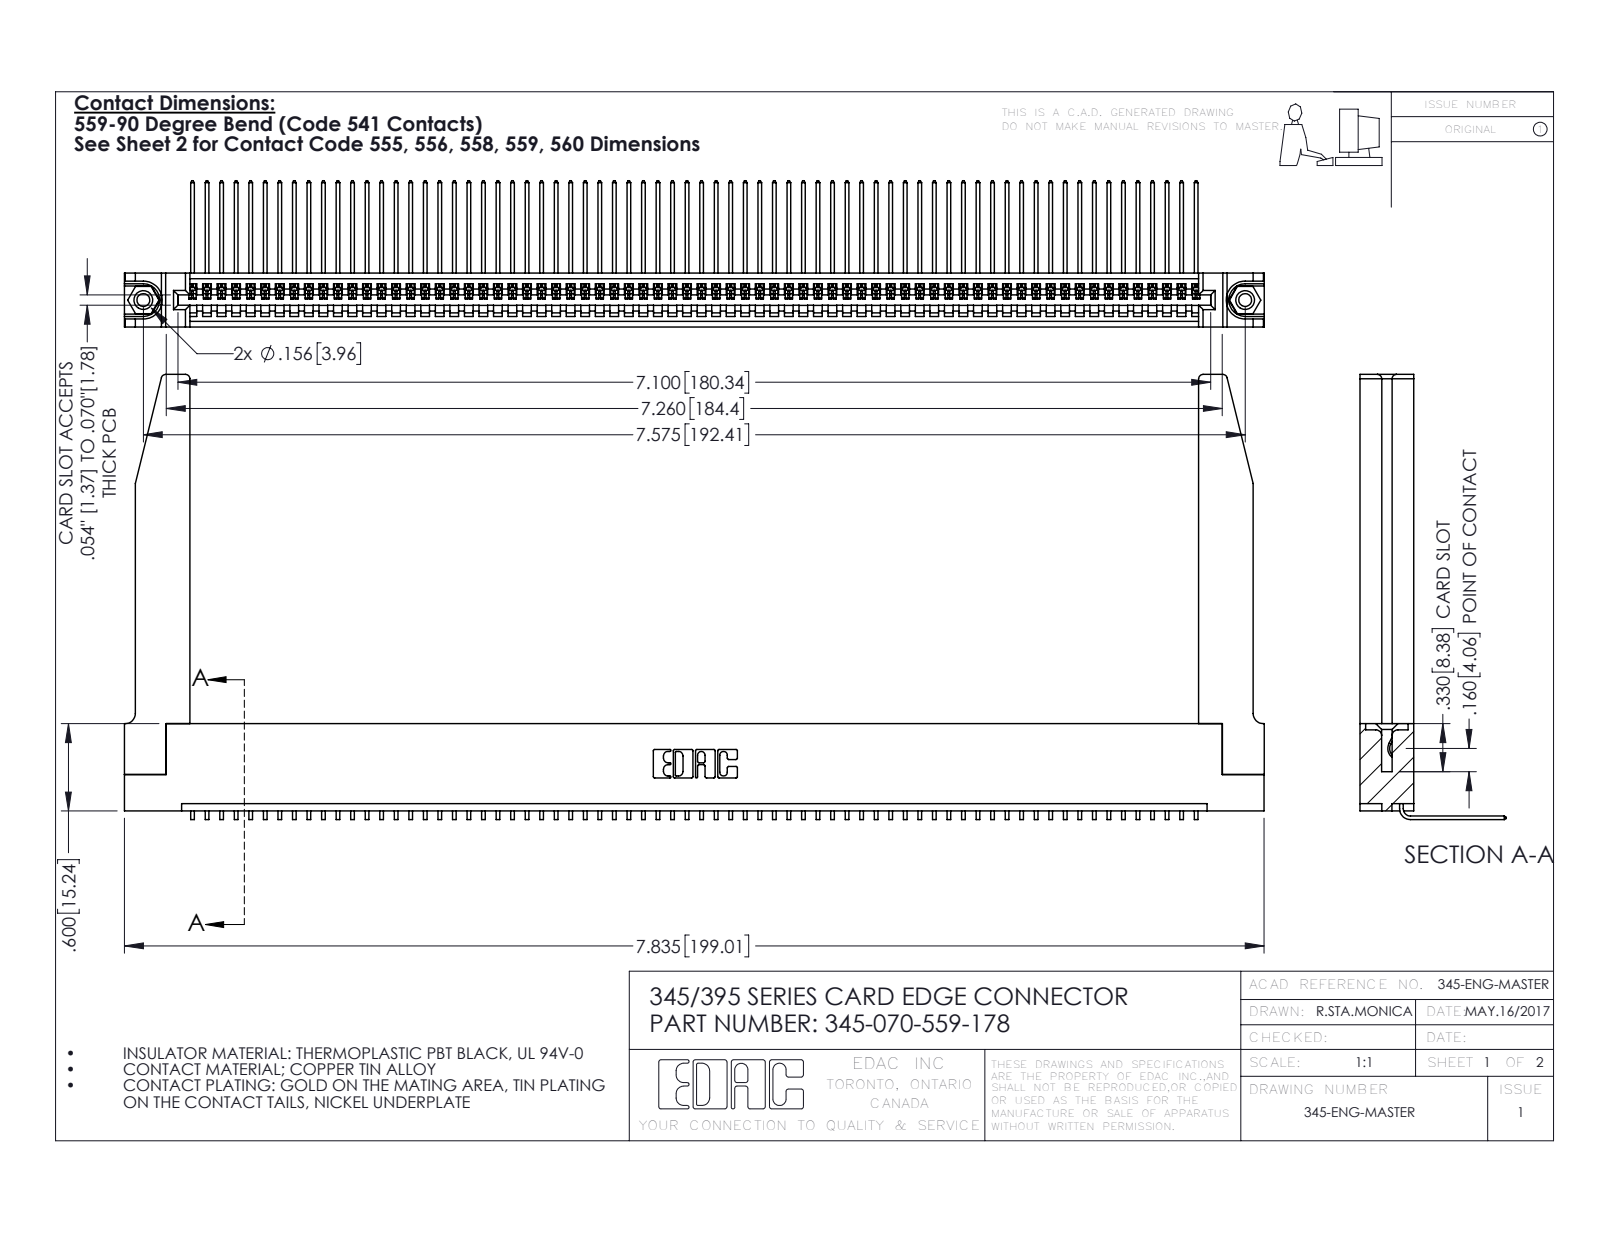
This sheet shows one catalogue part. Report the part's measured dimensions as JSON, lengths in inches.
{"part_name": "345-220-078_345-220-078; 345-250-001_345-250-001-102; 345 Part_Flush Mounting Lugs - 0.156 Dia-TH; 345-292-001_558 559 Tail - 1 (+1 more)", "step_written_by": "SolidWorks 2016 (CONFIG_CONTROL_DESIGN)", "units": "inches", "bodies": {"solids": 75, "faces": 4560, "planar": 3162, "cylindrical": 1346, "other": 52}, "overall_size": [7.836, 3.059, 1.005], "volume_in3": 1.656, "surface_area_in2": 53.22, "round_holes": [[0.089, 2], [0.125, 2], [0.156, 2], [0.064, 1]], "round_bosses_or_shafts": [[0.155, 2]], "partial_cylinders_radius": [[0.006, 140], [0.01, 22], [0.03, 8], [0.007, 6], [0.031, 6], [0.026, 3], [0.031, 2], [0.04, 2]], "face_to_face_distances": [0.072, 0.37, 0.298, 0.2, 0.098, 0.272, 0.025, 0.225, 0.149, 0.148], "hole_center_spacings": [0.27, 7.339, 7.575]}
